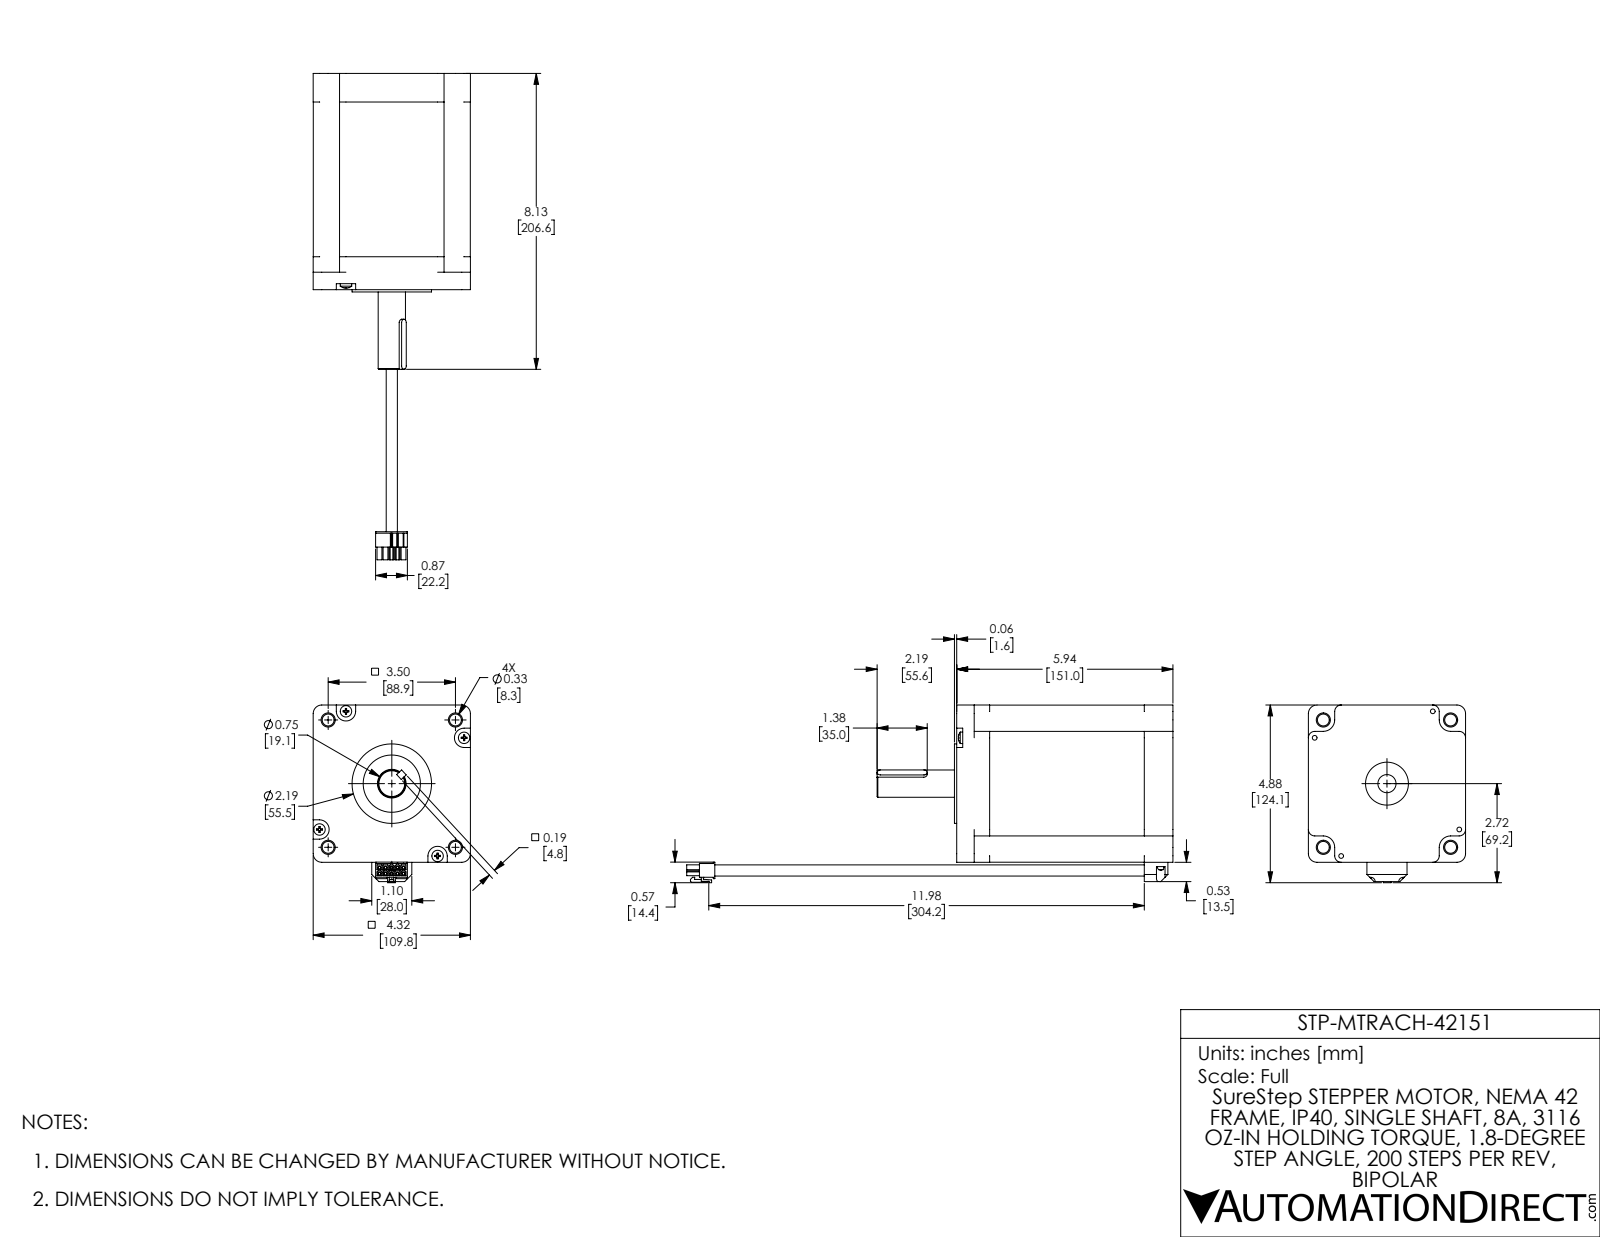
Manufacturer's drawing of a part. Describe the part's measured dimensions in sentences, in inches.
The part is named "STP-MTRAC-42151". Its 3-D file was written by "SolidWorks 2017 (AUTOMOTIVE_DESIGN)". It is 13 solids with 997 faces: 602 planar, 205 cylindrical and 190 other. Overall it measures 13.37 by 4.884 by 4.323 inches. Its volume is 50.24 cubic inches and its surface area 350.7 square inches. Round holes: 8 of diameter 0.177, 6 of diameter 0.13, 4 of diameter 0.181, 4 of diameter 0.327, 1 of diameter 0.591, 1 of diameter 0.787, 1 of diameter 1.116, 1 of diameter 1.181, 1 of diameter 1.378, 1 of diameter 1.575, 1 of diameter 1.627, 1 of diameter 2.047. Round bosses or shafts: 4 of diameter 0.315, 4 of diameter 0.157, 2 of diameter 0.177, 1 of diameter 2.579, 1 of diameter 2.559, 1 of diameter 2.186, 1 of diameter 1.207, 1 of diameter 1. Partial cylindrical surfaces (rounded edges, fillets, slot ends): 22 of radius 0.012, 16 of radius 0.177, 6 of radius 0.01, 4 of radius 0.236, 4 of radius 0.266, 4 of radius 0.315, 2 of radius 0.094, 2 of radius 0.118. The main face-to-face distances are 4.319, 4.321, 0.669, 5.945, 4.862, 0.787, 5.157, 4.252, 5.039, 0.906. The hole center spacings are 0.545, 2.354, 3.019, 3.329, 3.77, 4.799, 1.03, 2.475.
